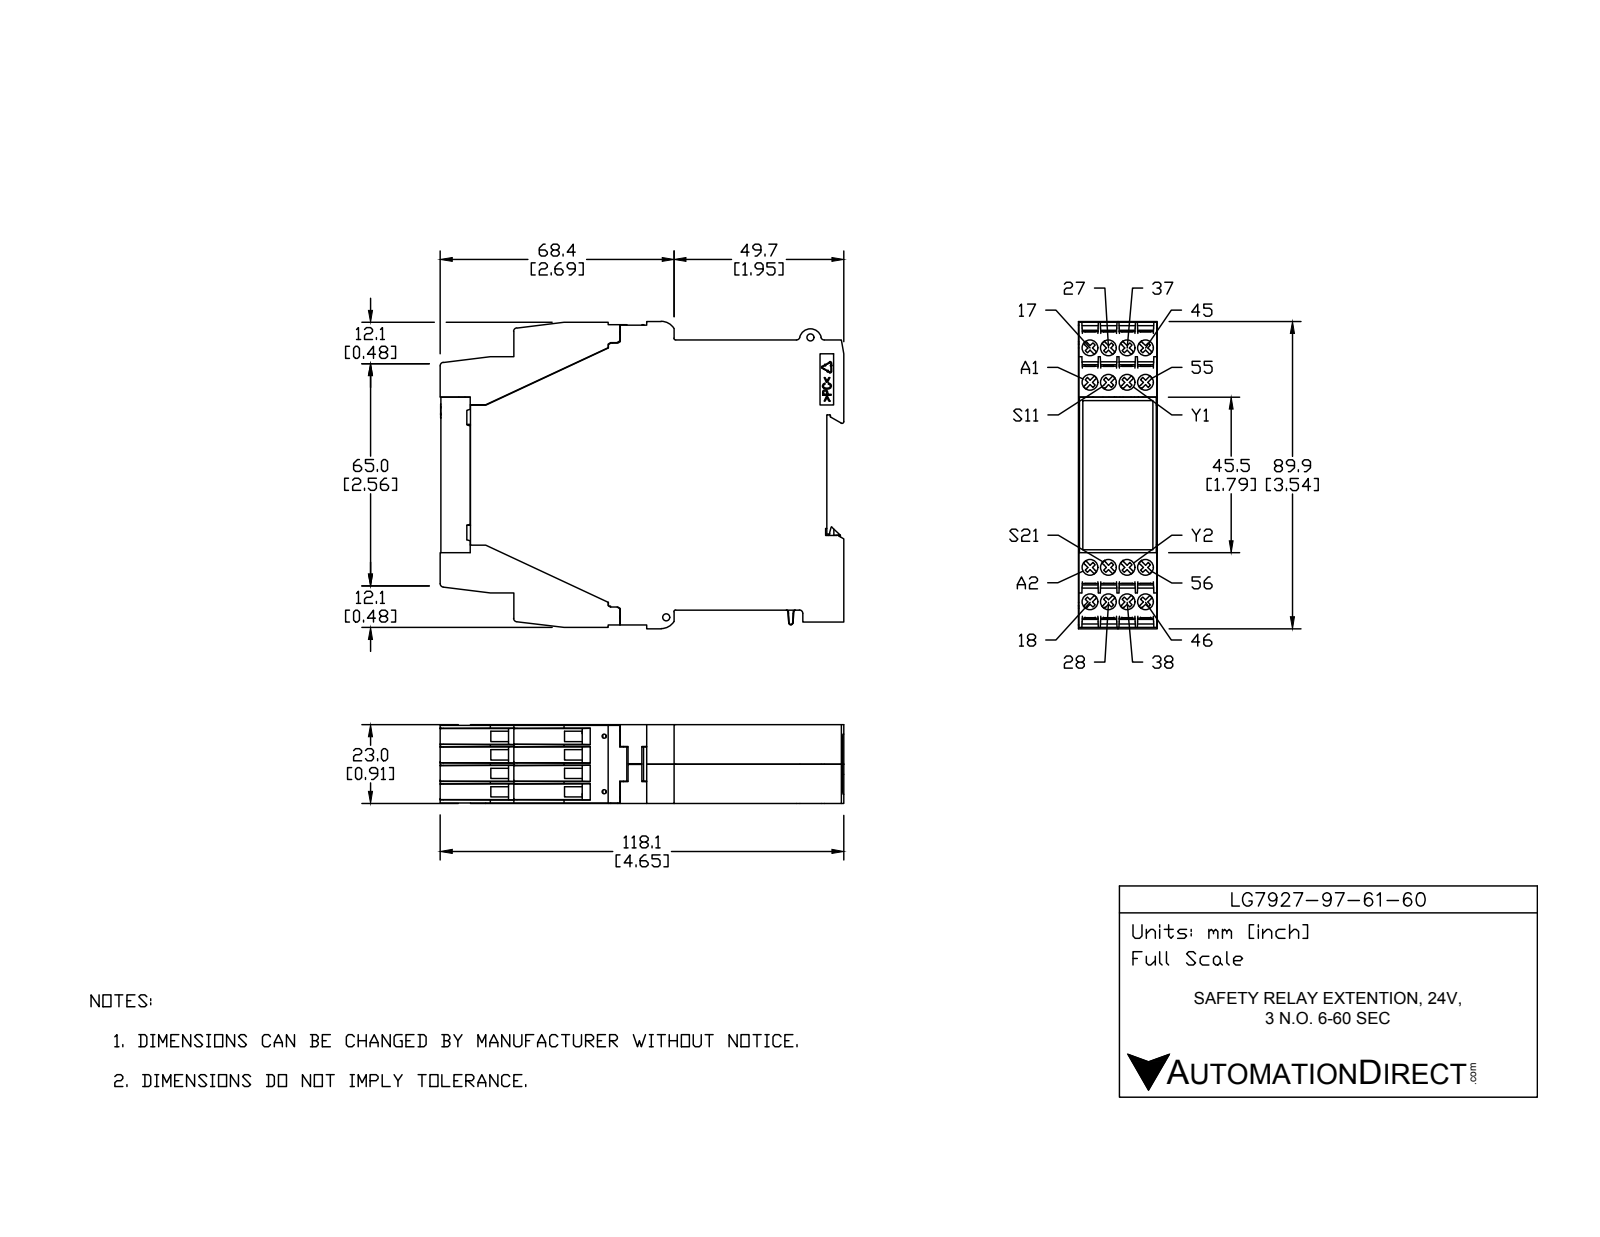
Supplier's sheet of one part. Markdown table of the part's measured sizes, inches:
| quantity | value |
| --- | --- |
| part name | LG7927-97-61-10 |
| STEP written by | SolidWorks 2017 (AUTOMOTIVE_DESIGN) |
| units | inches |
| bodies | 1 solid, 2054 faces (1604 planar, 319 cylindrical, 131 other) |
| overall size | 4.656 × 3.537 × 0.906 |
| volume | 12.64 in³ |
| surface area | 62.74 in² |
| round holes (diameter × count) | 0.181 × 16, 0.079 × 3, 0.047 × 2, 0.079 × 2 |
| round bosses / shafts (diameter × count) | 0.173 × 16, 0.087 × 1 |
| partial cylindrical surfaces (radius × count) | 0.008 × 52, 0.012 × 36, 0.02 × 31, 0.039 × 28, 0.006 × 6, 0.014 × 6, 0.174 × 2, 0.043 × 1 |
| main face-to-face distances | 0.906, 0.897, 0.894, 0.902, 4.451, 0.031, 0.874, 0.03, 0.039, 3.11 |
| hole center spacings | 0.213, 0.451, 2.541, 0.398, 0.425, 0.582, 2.531, 2.567 |
